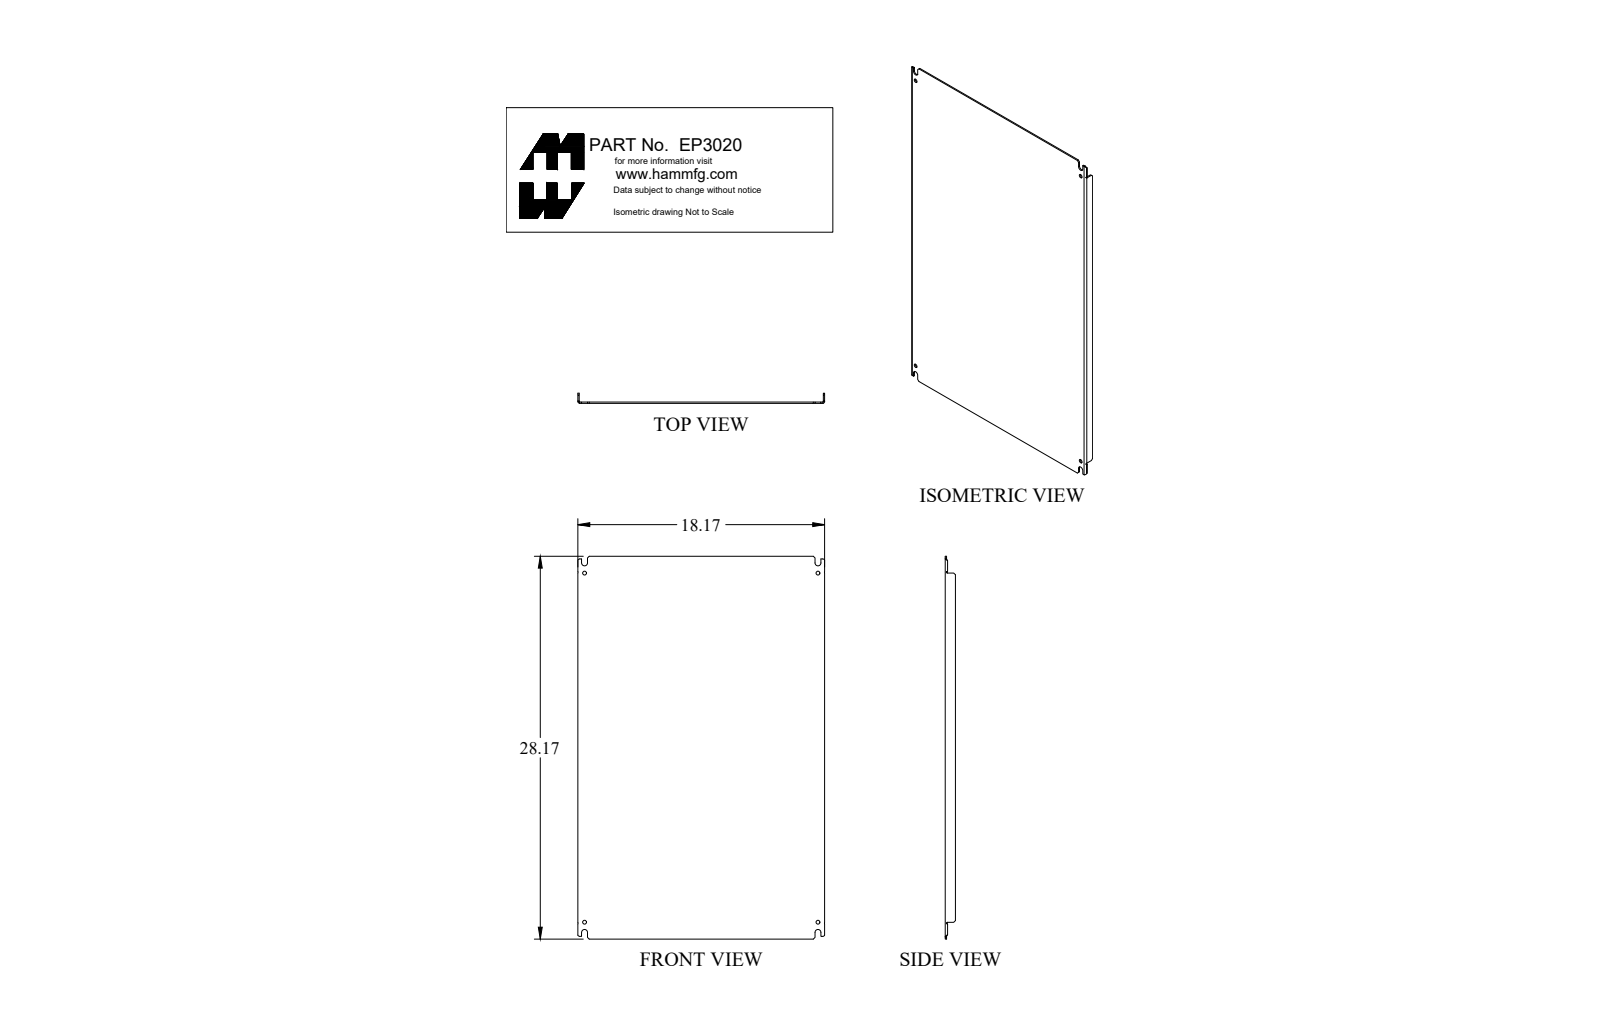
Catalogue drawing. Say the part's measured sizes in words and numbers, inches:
The part is named "EP3020". Its 3-D file was written by "SolidWorks 2018 (AUTOMOTIVE_DESIGN)". It is 1 solid with 84 faces: 50 planar, 26 cylindrical and 8 other. Overall it measures 28.17 by 18.17 by 0.75 inches. Its volume is 51.47 cubic inches and its surface area 1 093 square inches. Round holes: 4 of diameter 0.281. Partial cylindrical surfaces (rounded edges, fillets, slot ends): 4 of radius 0.219, 2 of radius 0.048, 2 of radius 0.062, 2 of radius 0.143. The main face-to-face distances are 0.095, 18.075, 17.98, 18.17, 0.75, 0.655, 28.17, 0.171, 0.076, 0.579. The hole center spacings are 17.188, 25.688, 30.908.
